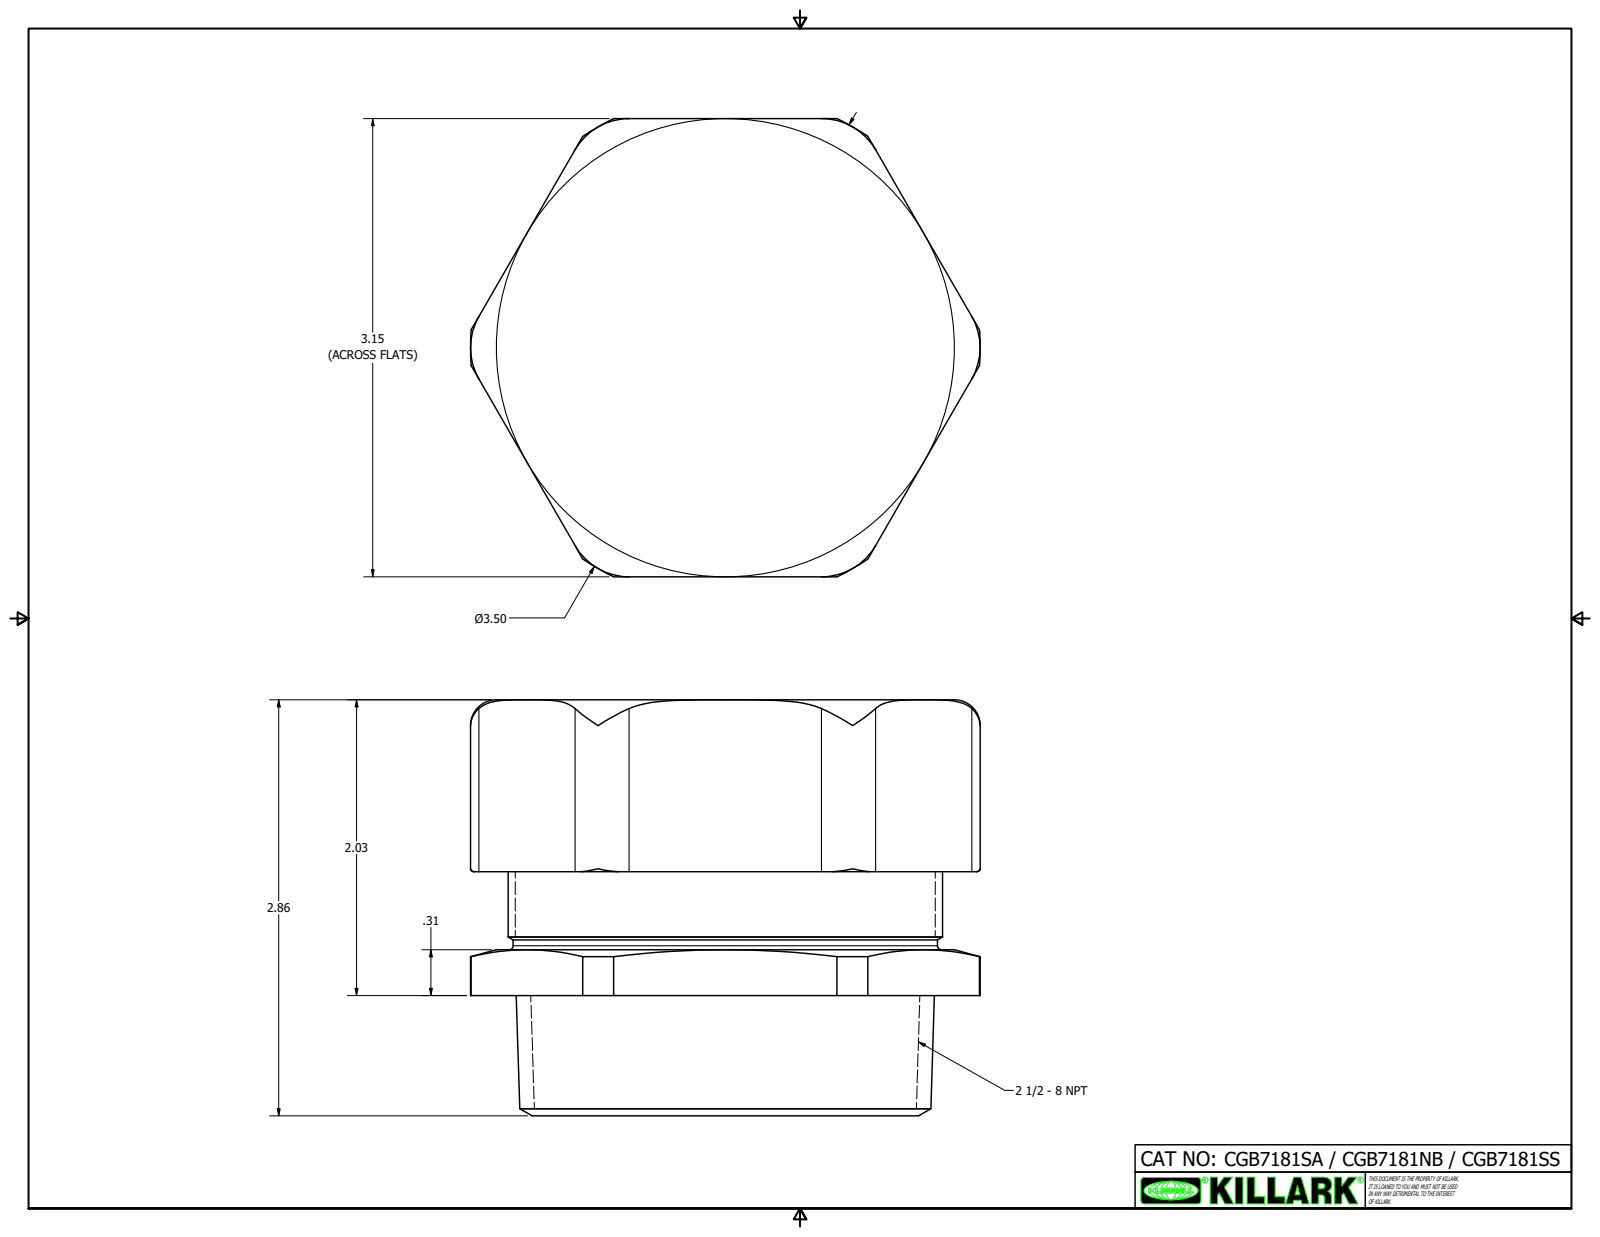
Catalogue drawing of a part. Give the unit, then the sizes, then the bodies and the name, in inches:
Units: inches
Overall size (bounding box): 3.504 × 3.15 × 2.859
Round bosses / shafts (diameter × count): ⌀2.986 ×1, ⌀2.918 ×1
Partial cylindrical surfaces — rounded edges, fillets, slot ends (radius × count): R0.43 ×6, R1.752 ×1
Main face-to-face distances: 3.15, 2.859, 0.827, 2.032, 1.678, 0.851, 1.181, 1.142, 0.315, 0.536
Volume: 21.73 in³ · Surface area: 47.89 in²
Bodies: 1 solid, 53 faces (17 planar, 14 cylindrical, 22 other)
Part name (STEP PRODUCT): CGB7181
STEP written by: Autodesk Inventor 2020 (AUTOMOTIVE_DESIGN)
